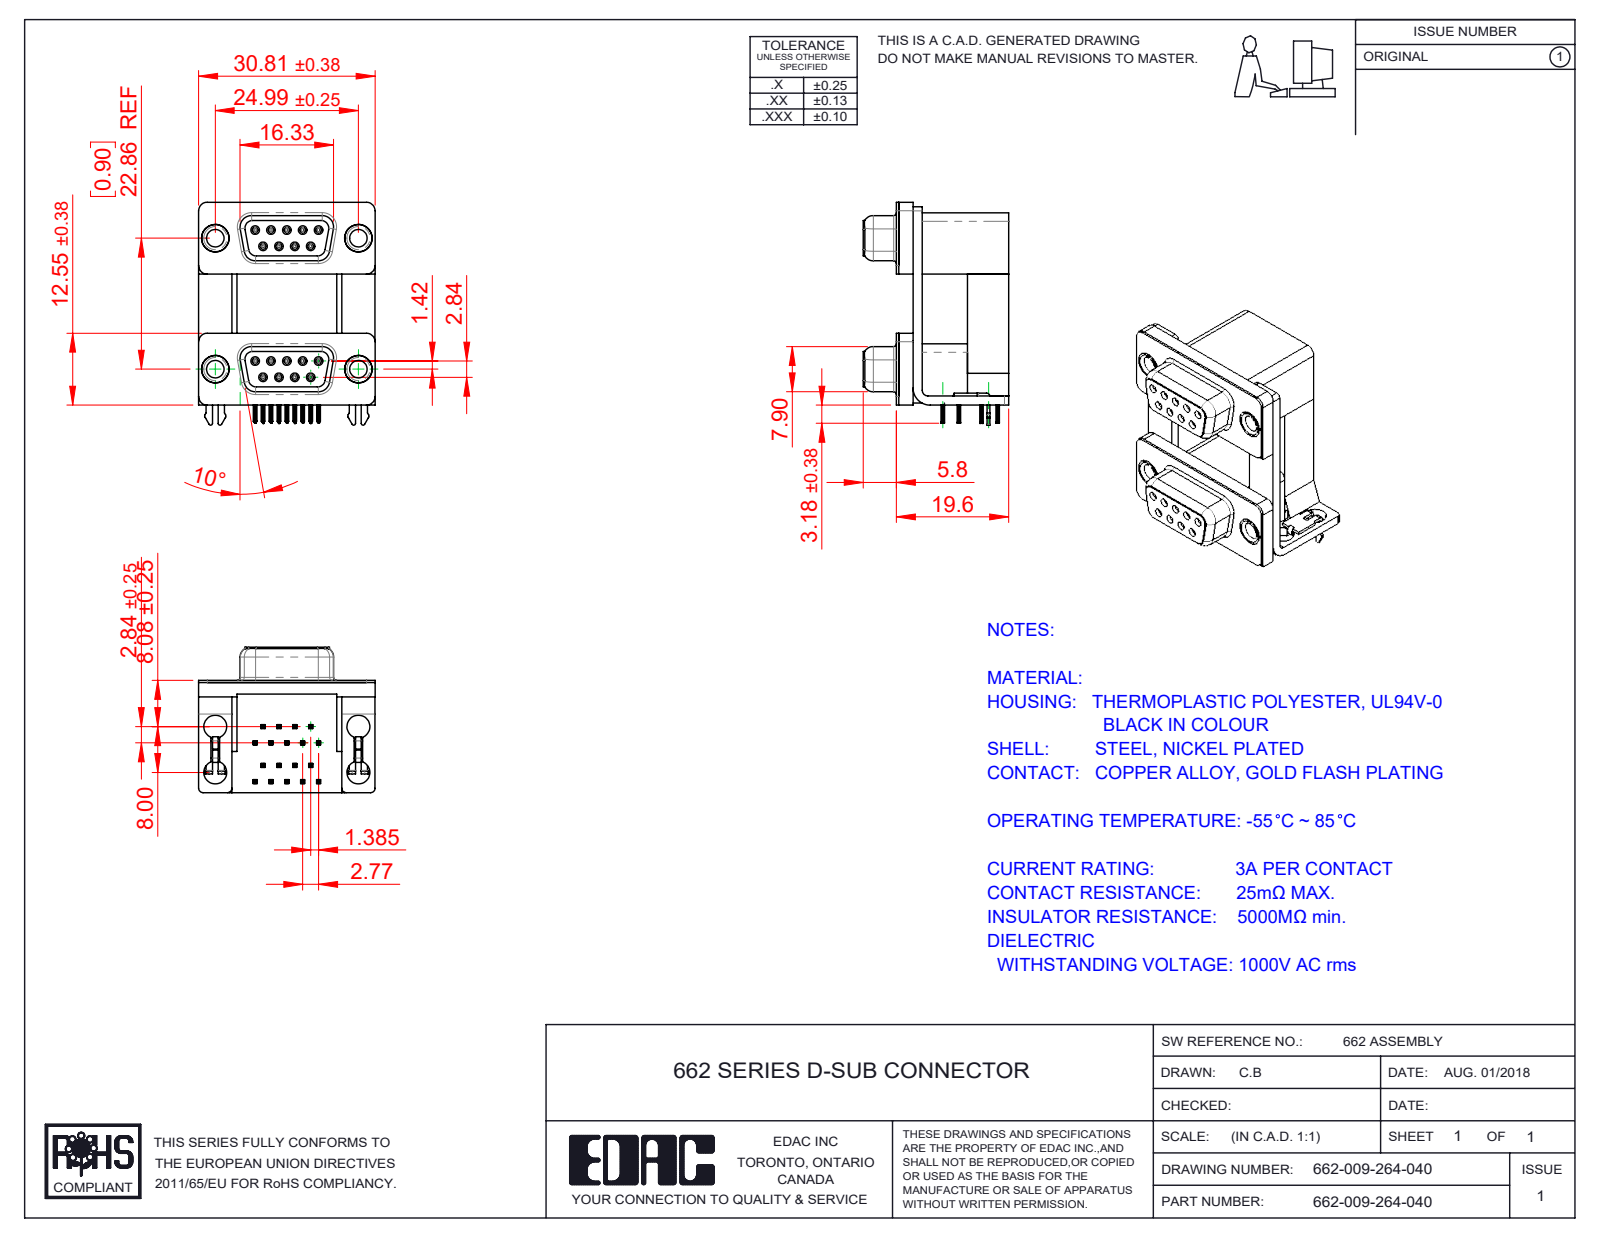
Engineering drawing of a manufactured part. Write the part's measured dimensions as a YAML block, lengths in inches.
part_name: "662 Contact Top Lower; 662 Contact Top Upper_H; 662 Contact Bottom Upper_H; 662 2 Prong Board Lock_4 (+8 more)"
step_written_by: "SolidWorks 2020 (CONFIG_CONTROL_DESIGN)"
units: inches
bodies: {solids: 31, faces: 3134, planar: 1452, cylindrical: 790, other: 892}
overall_size: [1.532, 1.213, 1]
volume: 0.72
surface_area: 21.44
round_holes:
  - {diameter: 0.031, count: 18}
  - {diameter: 0.035, count: 18}
  - {diameter: 0.157, count: 8}
  - {diameter: 0.12, count: 4}
  - {diameter: 0.138, count: 4}
  - {diameter: 0.189, count: 4}
  - {diameter: 0.197, count: 4}
round_bosses_or_shafts:
  - {diameter: 0.047, count: 18}
  - {diameter: 0.193, count: 4}
  - {diameter: 0.187, count: 4}
  - {diameter: 0.152, count: 4}
partial_cylinders:
  - {radius: 0.004, count: 145}
  - {radius: 0.006, count: 72}
  - {radius: 0.014, count: 36}
  - {radius: 0.013, count: 18}
  - {radius: 0.053, count: 16}
  - {radius: 0.059, count: 13}
  - {radius: 0.02, count: 12}
  - {radius: 0.03, count: 10}
face_to_face_distances: [0.098, 0.657, 0.756, 0.016, 0.9, 0.374, 0.283, 0.472, 0.114, 0.063]
hole_center_spacings: [0.124, 0.109, 0.907, 0.9, 0.218, 0.926, 0.79, 1.013]
